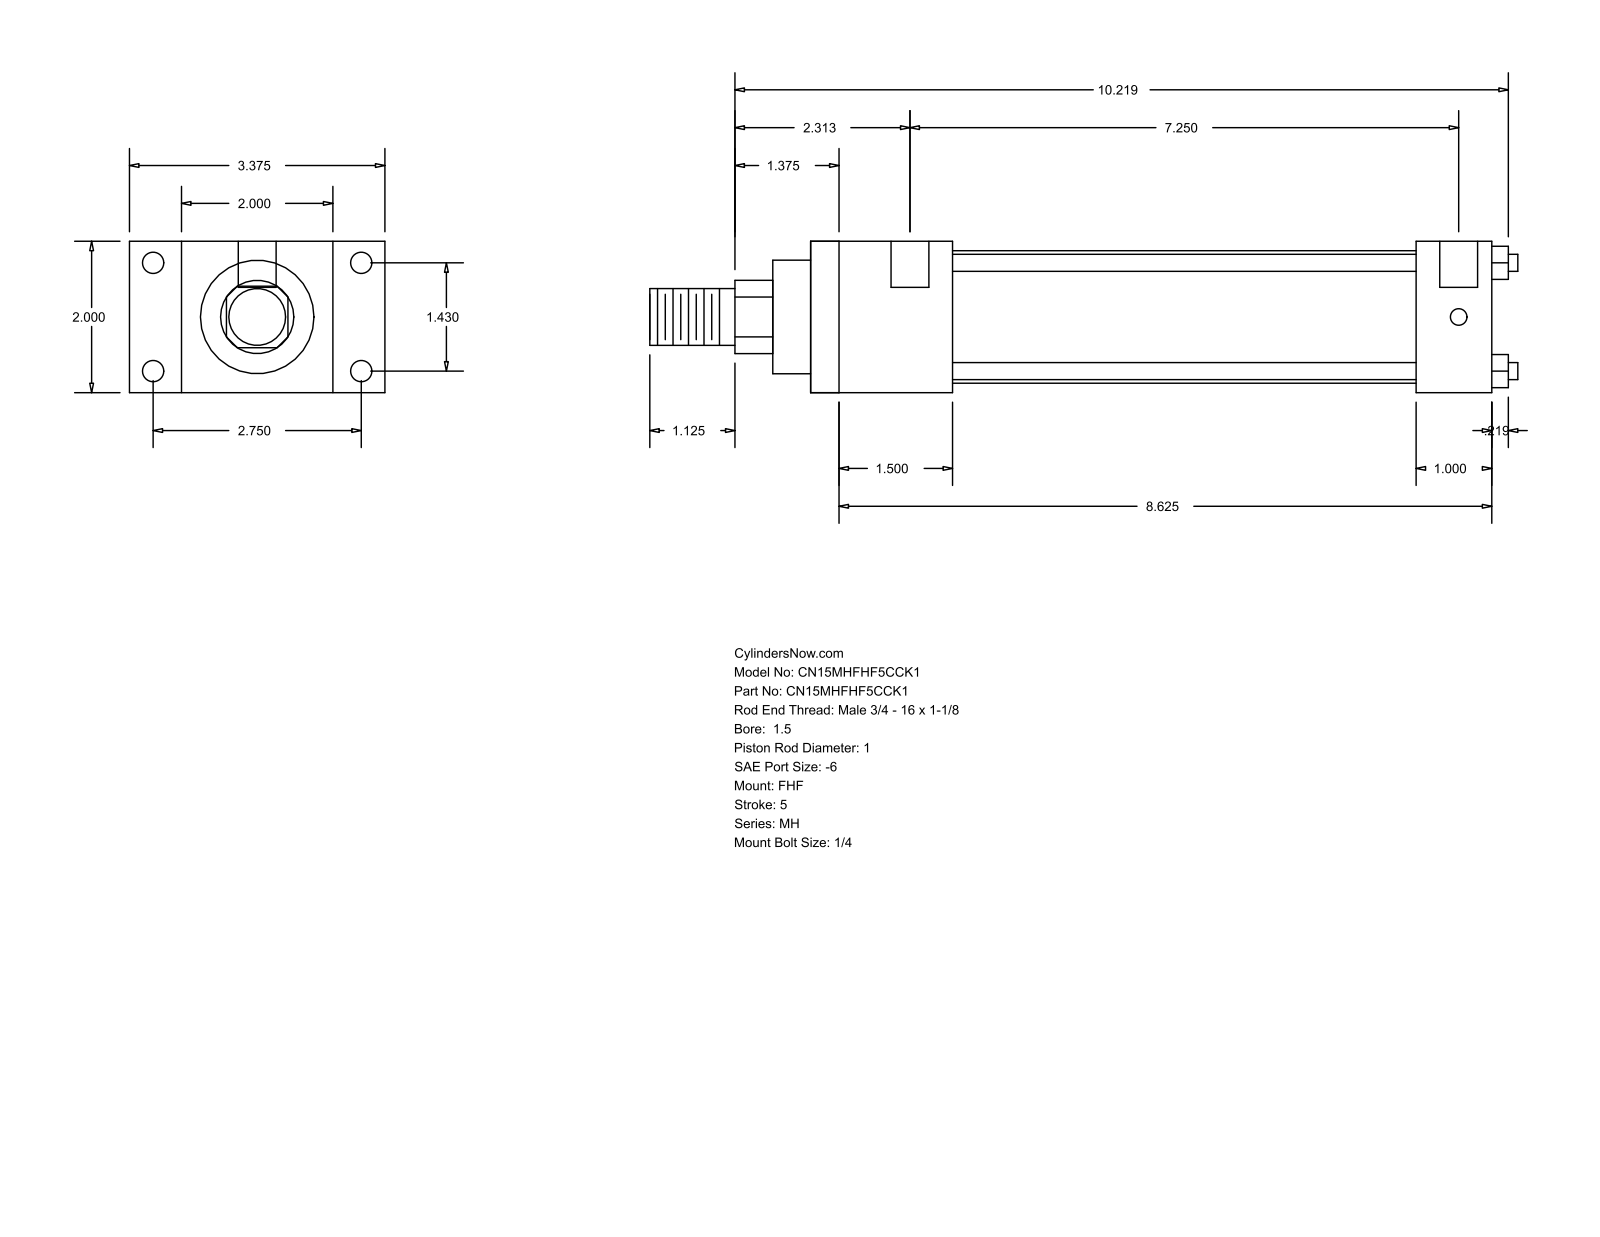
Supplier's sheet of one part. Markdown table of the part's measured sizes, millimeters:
| quantity | value |
| --- | --- |
| part name | MH_FHF__0150_1 |
| STEP written by | GSSL Pune (CONFIG_CONTROL_DESIGN) |
| units | millimeters |
| bodies | 0 solids, 88 faces (60 planar, 28 cylindrical, 0 other) |
| overall size | 291.31 × 85.72 × 50.8 |
| round holes (diameter × count) | 5.56 × 4, 7.14 × 4, 12.7 × 2 |
| round bosses / shafts (diameter × count) | 5.71 × 4, 44.45 × 1, 38.1 × 1, 25.4 × 1, 19.05 × 1 |
| partial cylindrical surfaces (radius × count) | 12.29 × 1 |
| main face-to-face distances | 50.8, 17.46, 68.26, 47.63, 85.72, 228.6, 180.97, 25.4, 203.2, 155.57 |
| hole center spacings | 36.32, 69.84, 78.72, 187.33, 3.18, 184.15 |
